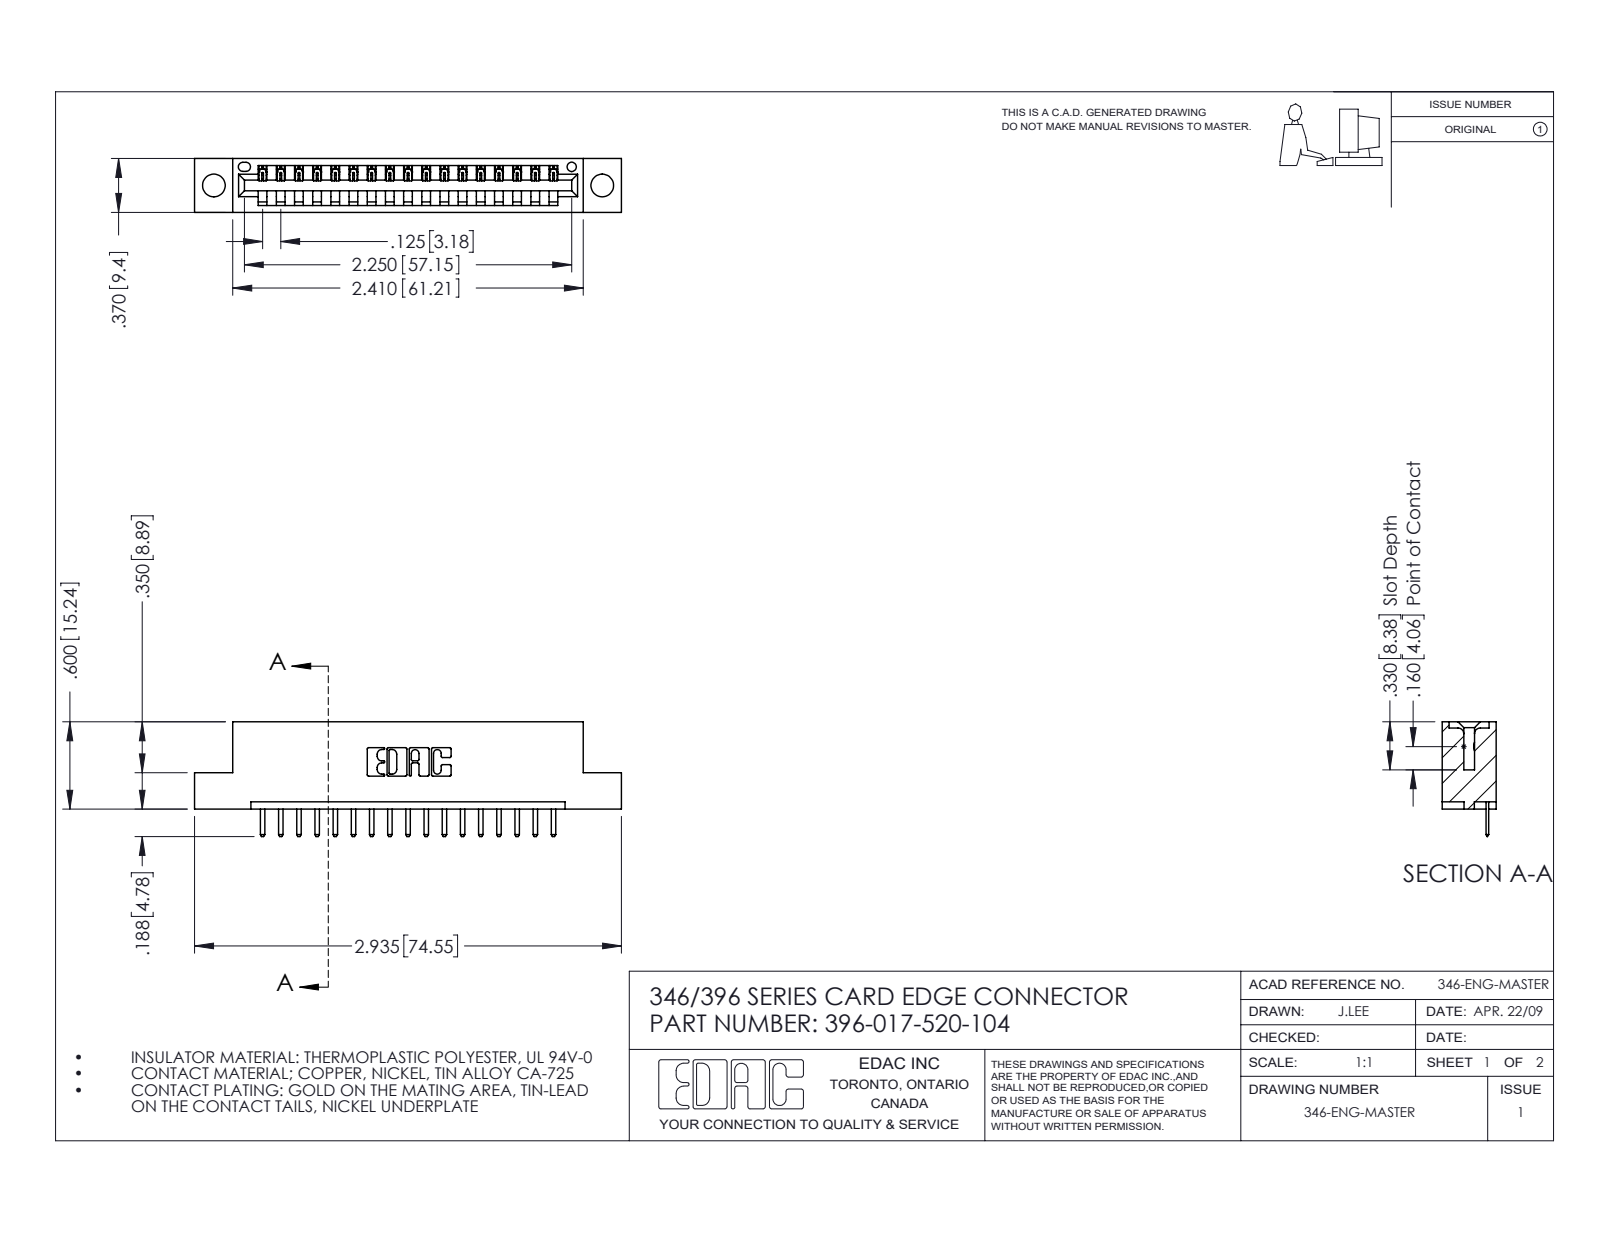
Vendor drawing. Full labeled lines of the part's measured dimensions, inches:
Part name (STEP PRODUCT): 346 Part_Flush Mounting Lugs - 0.156 Dia-TH; 345-292-001_345-293-120; 396-017-520-104
STEP written by: SolidWorks 2016 (CONFIG_CONTROL_DESIGN)
Units: inches
Bodies: 18 solids, 1176 faces (790 planar, 386 cylindrical, 0 other)
Overall size (bounding box): 2.935 × 0.788 × 0.37
Volume: 0.417 in³ · Surface area: 12.25 in²
Round holes (diameter × count): ⌀0.156 ×2, ⌀0.064 ×1
Partial cylindrical surfaces — rounded edges, fillets, slot ends (radius × count): R0.01 ×36, R0.006 ×34, R0.01 ×22, R0.007 ×6, R0.031 ×6, R0.026 ×3, R0.031 ×2, R0.04 ×2
Main face-to-face distances: 0.048, 0.322, 0.37, 0.25, 0.148, 0.222, 0.1, 0.174, 0.072, 0.298
Hole centre spacings: 0.246, 2.463, 2.67
